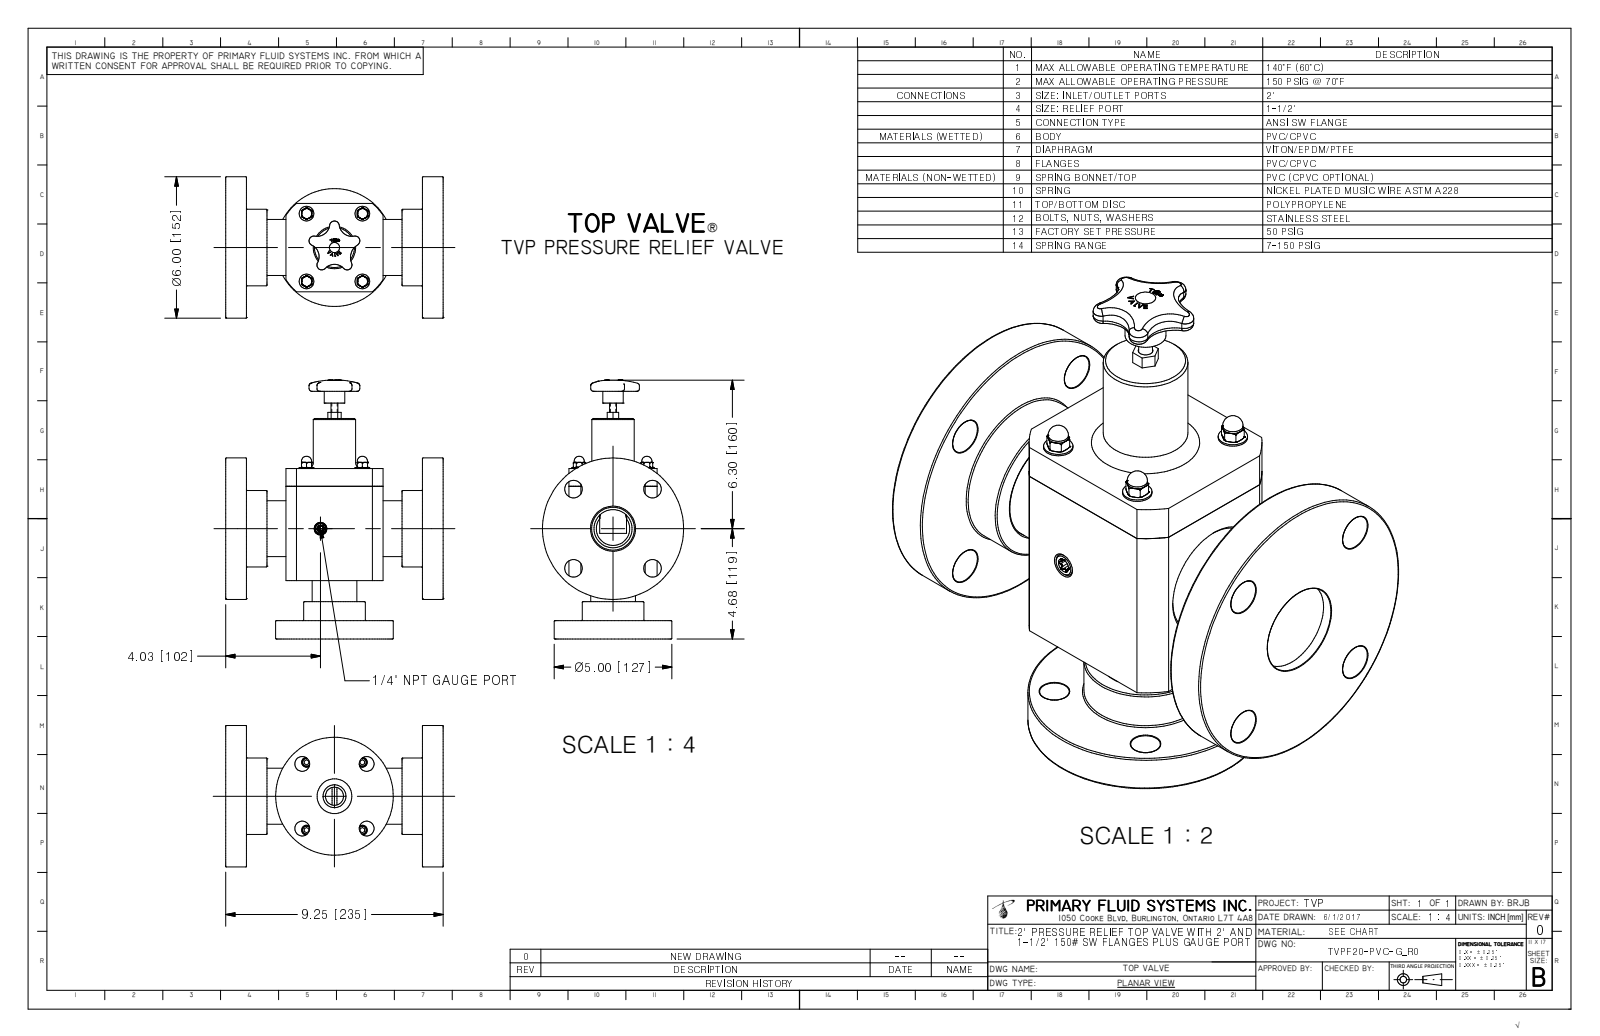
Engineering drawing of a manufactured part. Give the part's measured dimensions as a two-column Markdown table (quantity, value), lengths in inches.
| quantity | value |
| --- | --- |
| part name | TVPF20-PVC-G_R0 |
| STEP written by | Autodesk Inventor 2009 (AUTOMOTIVE_DESIGN) |
| units | inches |
| bodies | 1 solid, 469 faces (171 planar, 88 cylindrical, 210 other) |
| overall size | 10.982 × 9.25 × 6 |
| volume | 140.6 in³ |
| surface area | 483.7 in² |
| round holes (diameter × count) | 0.175 × 4, 0.63 × 4, 0.745 × 4, 0.188 × 1, 0.437 × 1, 0.77 × 1, 1.476 × 1, 1.5 × 1, 1.856 × 1, 1.913 × 1, 1.939 × 1 |
| round bosses / shafts (diameter × count) | 0.625 × 4, 0.433 × 4, 0.375 × 4, 6 × 1, 5 × 1, 3.244 × 1, 2.62 × 1, 2.375 × 1 |
| partial cylindrical surfaces (radius × count) | 0.027 × 6, 0.085 × 5, 0.205 × 5, 0.536 × 4, 0.656 × 4, 0.625 × 1, 0.745 × 1, 2.475 × 1 |
| main face-to-face distances | 0.885, 8.365, 9.25, 7.48, 2.563, 6.688, 1.678, 5.803, 3.75, 0.78 |
| hole center spacings | 1.937, 2.375, 2.558, 2.74, 3.359, 0.194, 0.195, 1.864 |
